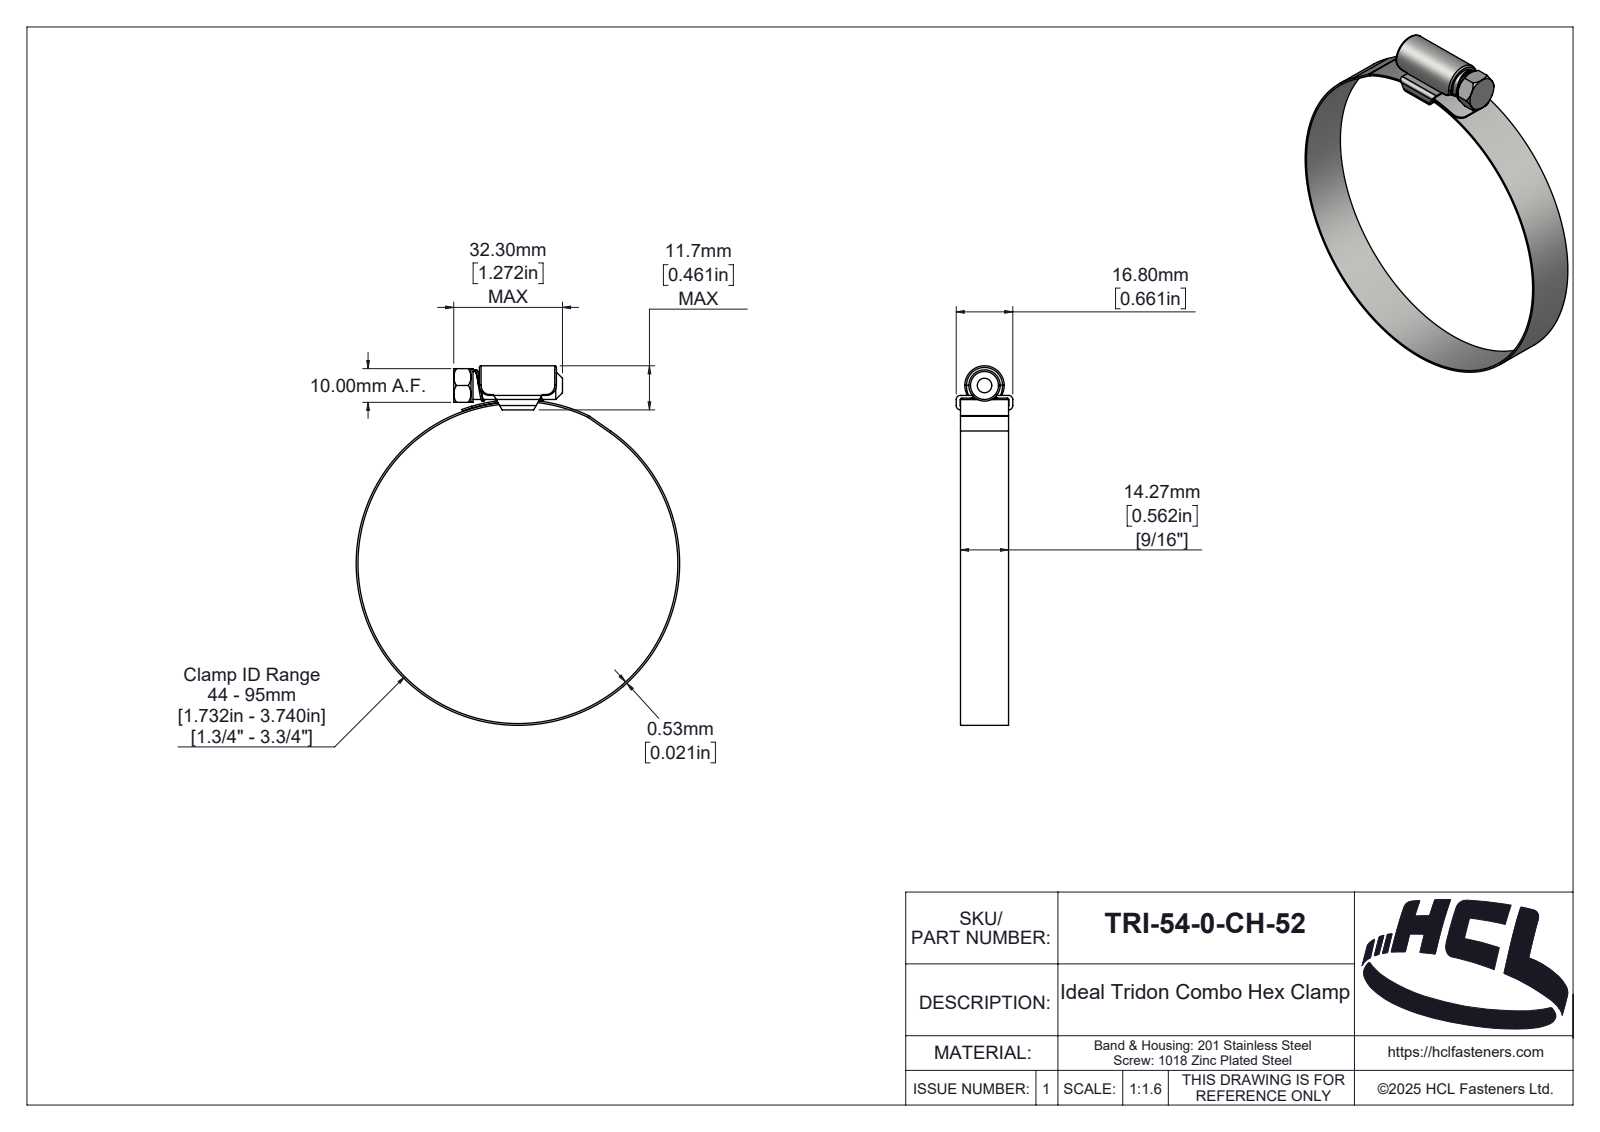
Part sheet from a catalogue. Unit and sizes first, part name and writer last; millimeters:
Units: millimetres
Overall size (bounding box): 106.73 × 96.06 × 16.8
Round holes (diameter × count): ⌀95 ×1
Round bosses / shafts (diameter × count): ⌀96.06 ×1, ⌀10 ×1, ⌀8.3 ×1
Partial cylindrical surfaces — rounded edges, fillets, slot ends (radius × count): R0.5 ×6, R3 ×4, R0.1 ×2, R1.2 ×2, R1.3 ×2, R0.46 ×1, R1.89 ×1, R2 ×1
Main face-to-face distances: 1.2, 14.26, 0.53, 3.5, 2.3, 4.3, 3.1, 0.8, 9.99, 1.27
Volume: 5 285 mm³ · Surface area: 12 377 mm²
Bodies: 3 solids, 212 faces (35 planar, 101 cylindrical, 76 other)
Part name (STEP PRODUCT): TRI-54-0-CH-52
STEP written by: SolidWorks 2025 (AUTOMOTIVE_DESIGN)
